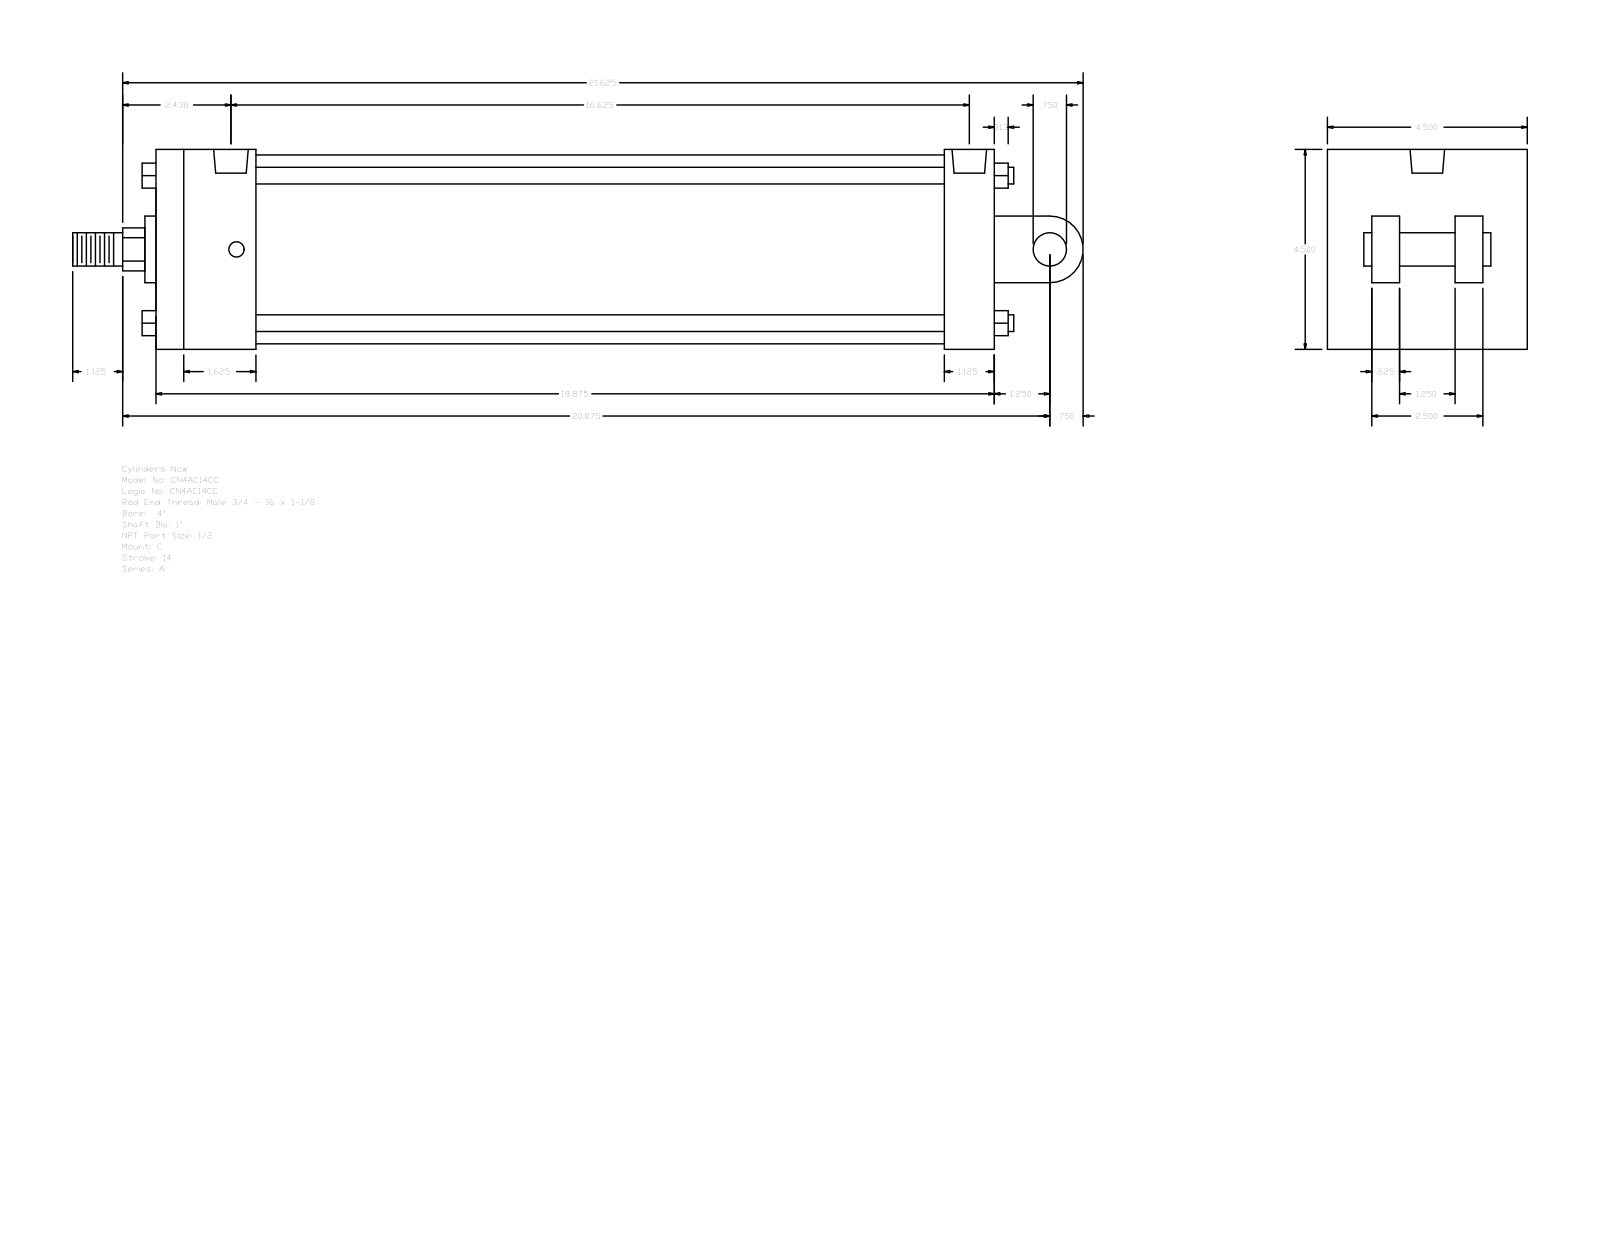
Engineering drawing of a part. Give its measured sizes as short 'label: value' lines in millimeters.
name: A_C__0400_1
written by: GSSL Pune (CONFIG_CONTROL_DESIGN)
unit: mm
bodies: 0 solids, 135 faces (102 planar, 33 cylindrical, 0 other)
size: 577.85 × 114.3 × 114.3
holes: 4× ⌀8.73, 2× ⌀19.77
bosses: 4× ⌀9.53, 2× ⌀19.05, 1× ⌀107.95, 1× ⌀38.1, 1× ⌀25.4
rounds: 1× R12.29, 1× R19.05
face distances: 114.3, 479.43, 73.03, 450.85, 28.58, 57.15, 393.7, 422.28, 41.27, 38.1
hole spacings: 3.18, 415.92, 419.1, 422.28
